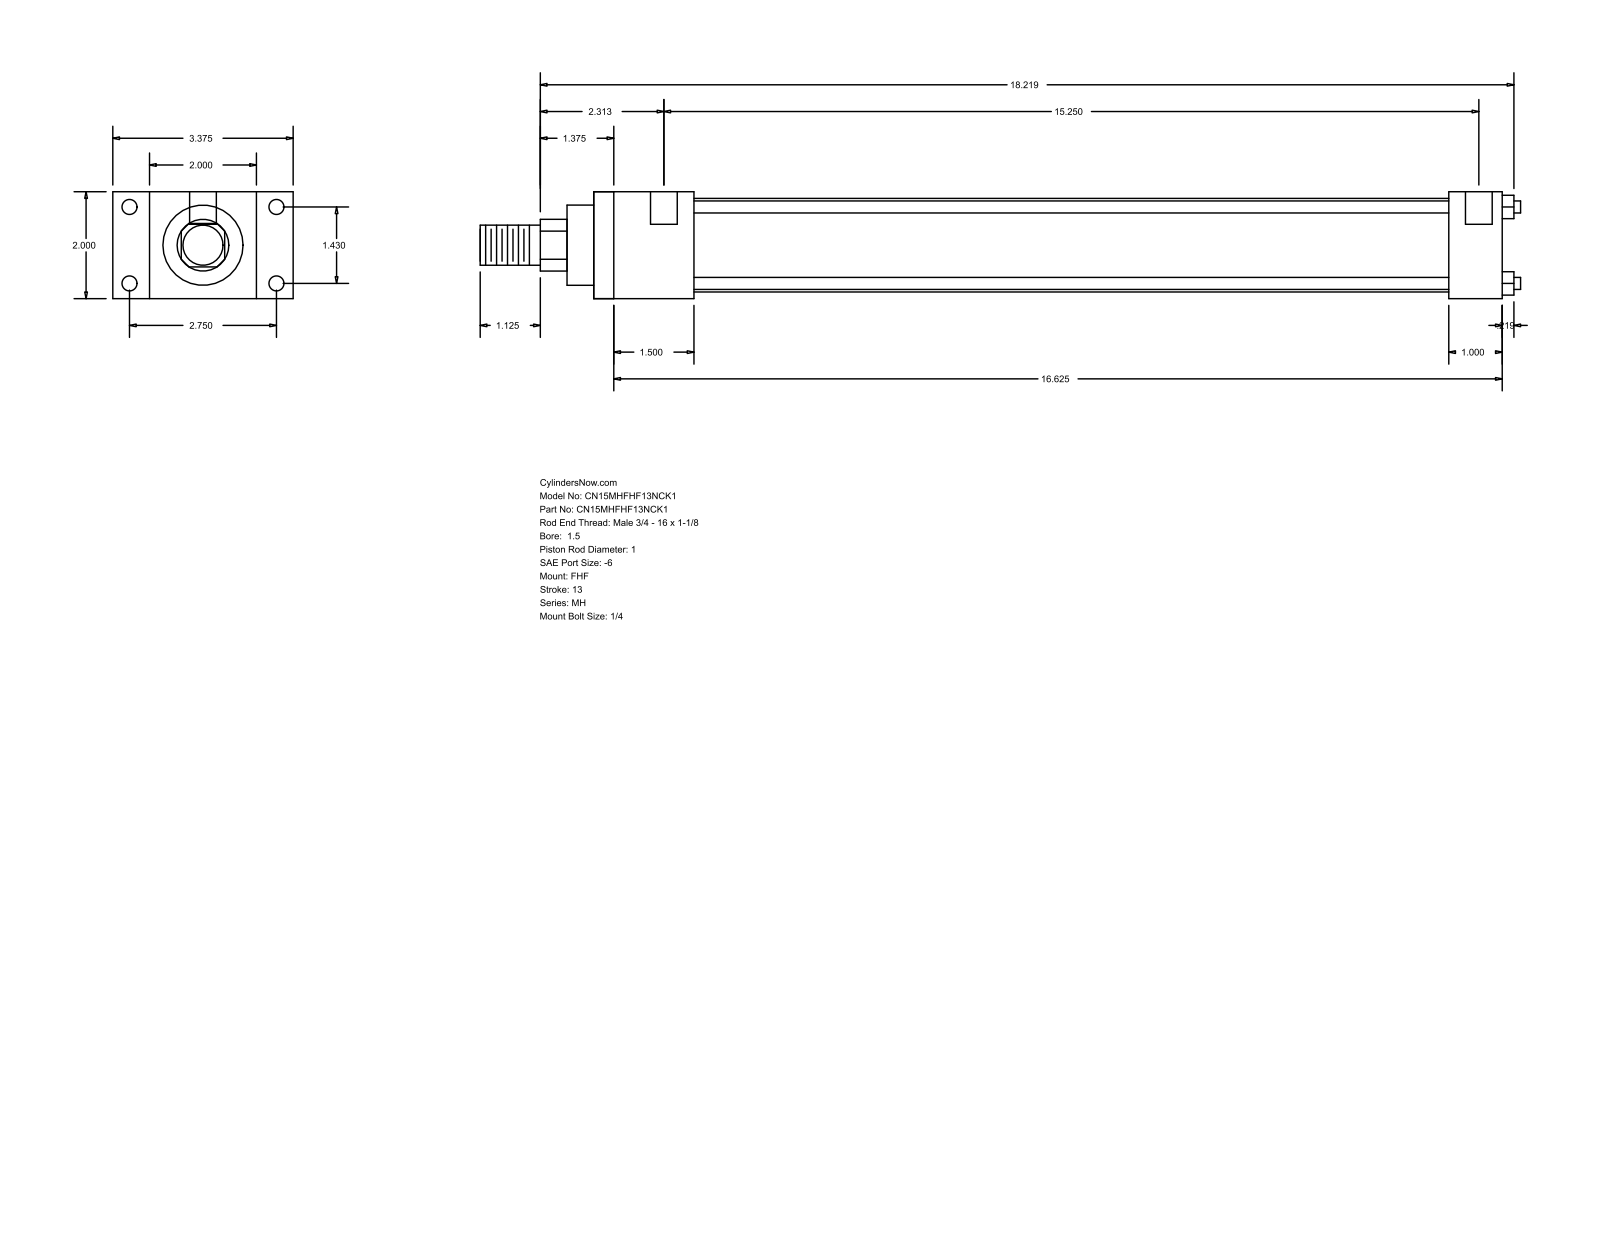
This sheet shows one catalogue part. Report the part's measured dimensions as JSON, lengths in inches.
{"part_name": "MH_FHF__0150_1", "step_written_by": "GSSL Pune (CONFIG_CONTROL_DESIGN)", "units": "inches", "bodies": {"solids": 0, "faces": 88, "planar": 60, "cylindrical": 28, "other": 0}, "overall_size": [19.469, 3.375, 2], "round_holes": [[0.219, 4], [0.281, 4], [0.5, 2]], "round_bosses_or_shafts": [[0.225, 4], [1.75, 1], [1.5, 1], [1, 1], [0.75, 1]], "partial_cylinders_radius": [[0.484, 1]], "face_to_face_distances": [2, 0.687, 2.687, 1.875, 3.375, 17, 15.125, 1, 16, 14.125], "hole_center_spacings": [1.43, 2.75, 3.099, 15.375, 0.125, 15.25]}
